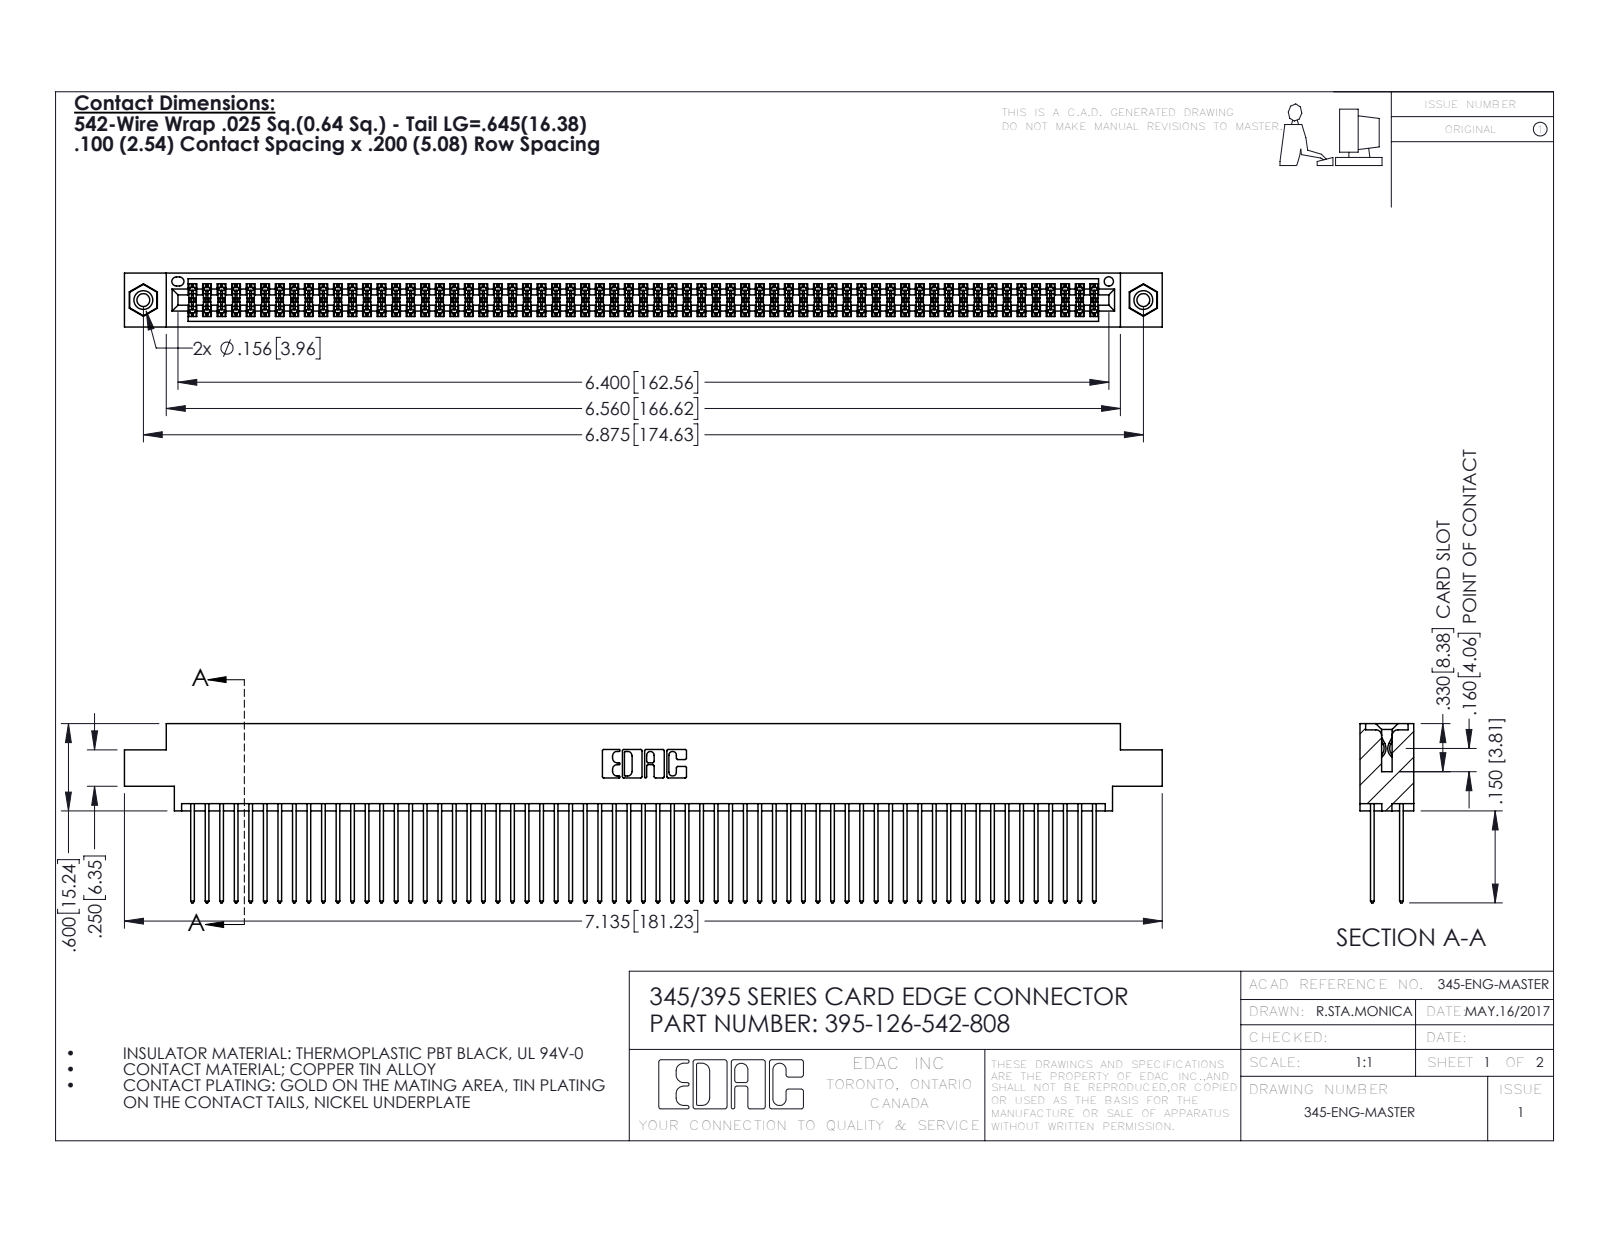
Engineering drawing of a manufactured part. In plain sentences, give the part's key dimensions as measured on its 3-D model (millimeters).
The part is named "395-126-542-808; 345-292-001_345-293-142; 345 Part_0.170 Offset - 0.156 Dia-TI; 345-250-001_345-250-003-102". Its 3-D file was written by "SolidWorks 2016 (CONFIG_CONTROL_DESIGN)". It is 129 solids with 6490 faces: 4274 planar, 2200 cylindrical and 16 other. Overall it measures 181.2 by 31.3 by 9.4 millimeters. Its volume is 18 270 cubic millimeters and its surface area 30 310 square millimeters. Round holes: 2 of diameter 2.3, 2 of diameter 3.2, 2 of diameter 4, 1 of diameter 1.6. Round bosses or shafts: 2 of diameter 3.9. Partial cylindrical surfaces (rounded edges, fillets, slot ends): 189 of radius 0.2, 126 of radius 0.3, 22 of radius 0.3, 6 of radius 0.2, 6 of radius 0.8, 3 of radius 0.7, 2 of radius 0.4, 2 of radius 0.5. The main face-to-face distances are 1.8, 7.6, 5.1, 2.5, 6.9, 0.6, 9.4, 5.7, 4.4, 3.8. The hole center spacings are 6.9, 168.6, 174.6.
